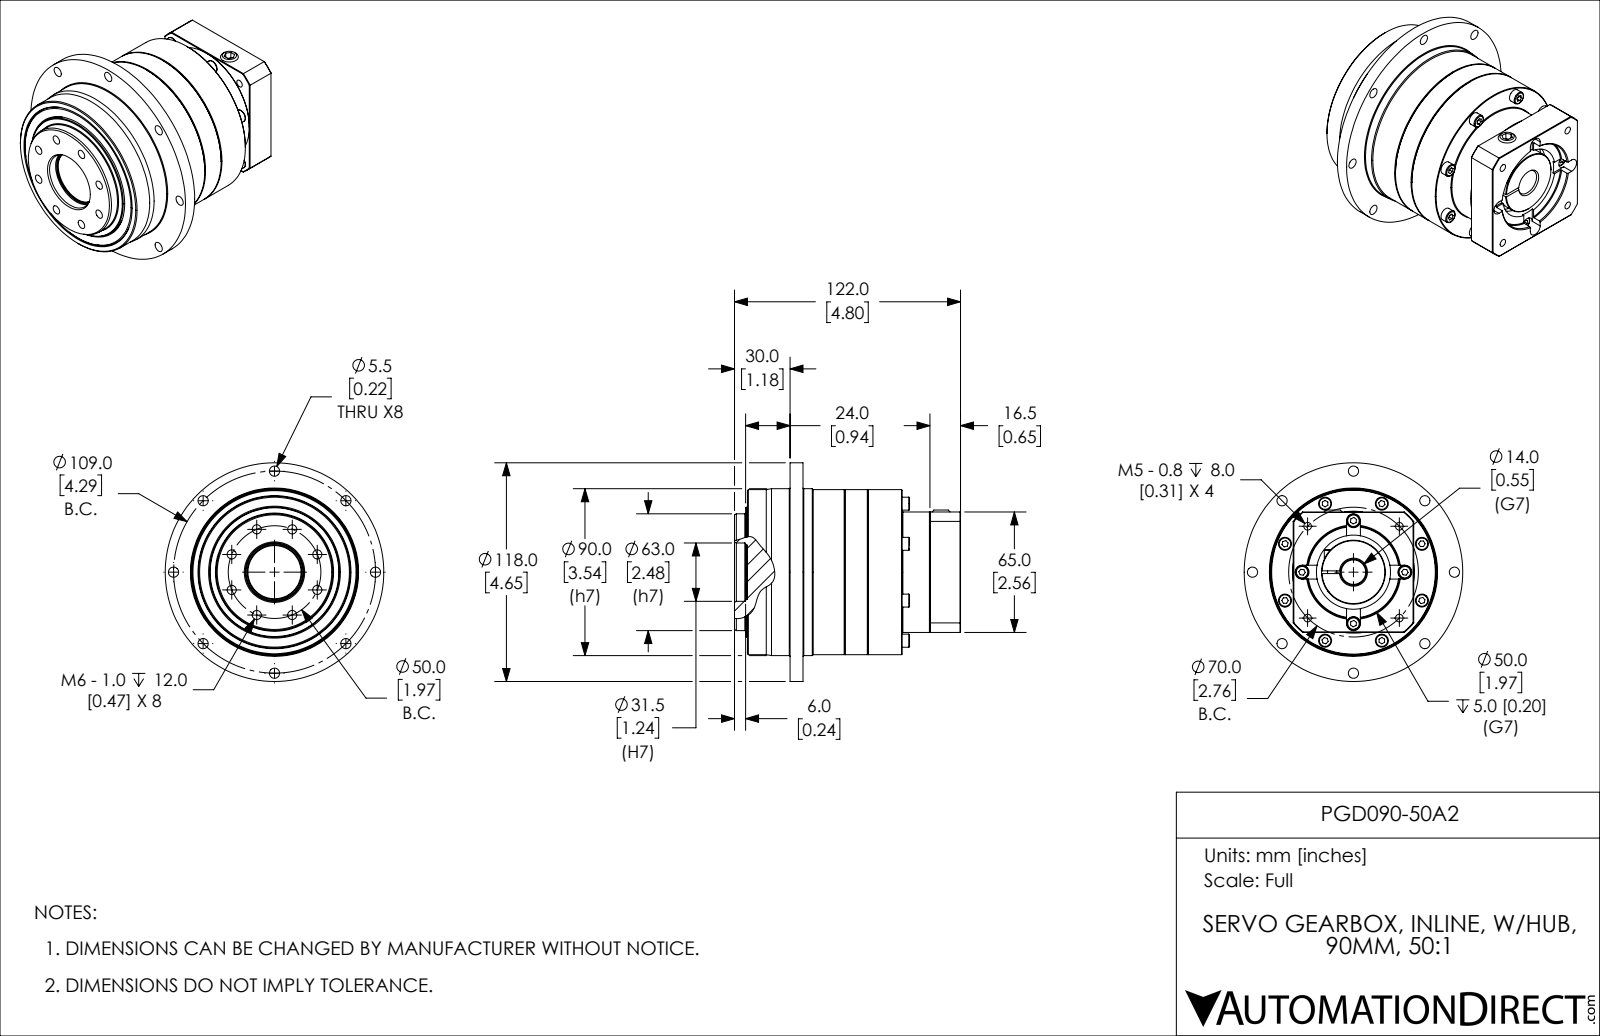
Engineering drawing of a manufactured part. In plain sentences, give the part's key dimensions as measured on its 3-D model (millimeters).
The part is named "PGD090-50A2". Its 3-D file was written by "SolidWorks 2015 (AUTOMOTIVE_DESIGN)". It is 5 solids with 502 faces: 259 planar, 150 cylindrical and 93 other. Overall it measures 122.02 by 118 by 118 millimeters. Its volume is 672 607 cubic millimeters and its surface area 75 167 square millimeters. Round holes: 8 of diameter 5.5, 7 of diameter 4.92, 4 of diameter 4.13, 4 of diameter 5, 4 of diameter 7.5, 1 of diameter 4.92, 1 of diameter 8, 1 of diameter 8.5, 1 of diameter 14, 1 of diameter 18, 1 of diameter 20, 1 of diameter 31.5. Round bosses or shafts: 12 of diameter 7, 1 of diameter 118, 1 of diameter 90, 1 of diameter 89, 1 of diameter 65, 1 of diameter 63, 1 of diameter 42, 1 of diameter 32. Partial cylindrical surfaces (rounded edges, fillets, slot ends): 1 of radius 4.75, 1 of radius 42.5. The main face-to-face distances are 4, 23, 27, 94.52, 60.52, 64.52, 87.52, 27.5, 88.02, 92.02. The hole center spacings are 32.83, 68.11, 78.19, 25, 10.64, 15.27, 24.93, 29.4.
